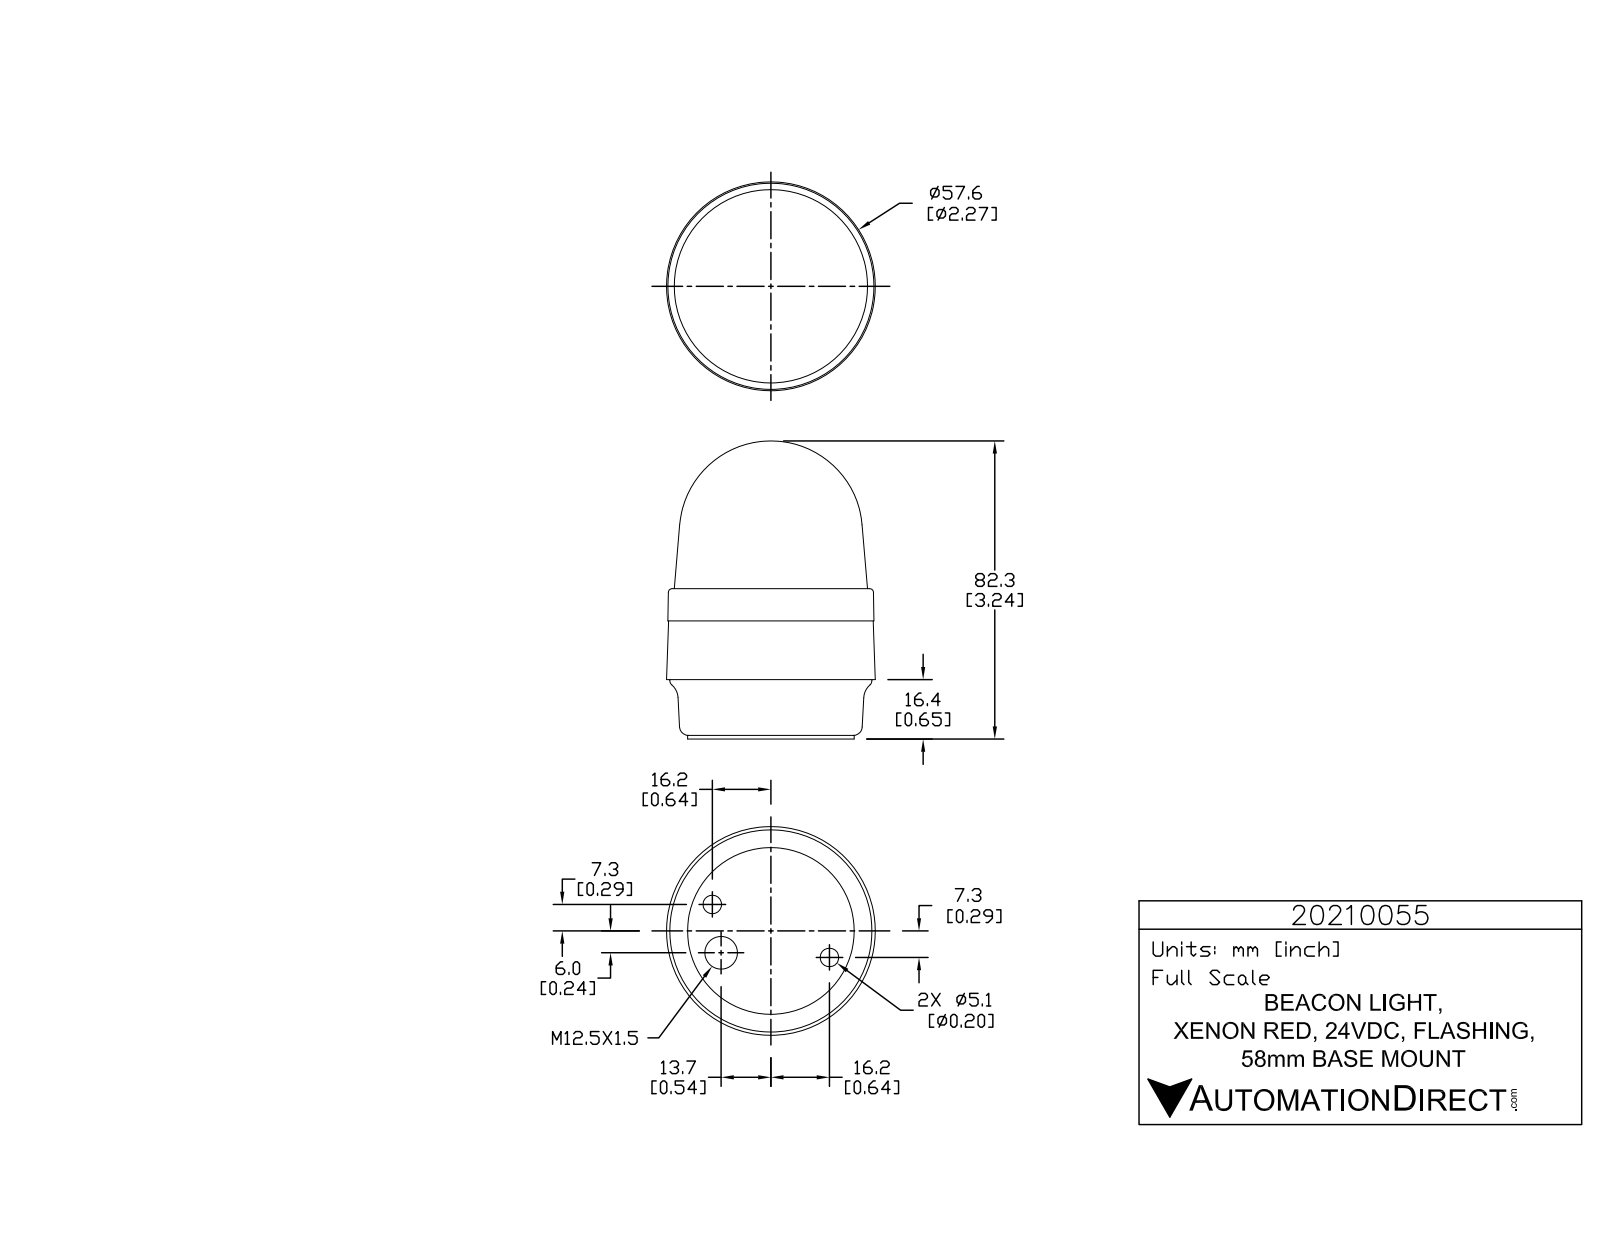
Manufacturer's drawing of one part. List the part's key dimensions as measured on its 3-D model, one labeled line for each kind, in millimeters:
Part name (STEP PRODUCT): 20210055
STEP written by: SolidWorks 2015 (AUTOMOTIVE_DESIGN)
Units: millimetres
Bodies: 1 solid, 763 faces (527 planar, 145 cylindrical, 91 other)
Overall size (bounding box): 82.3 × 57.63 × 57.63
Volume: 164 395 mm³ · Surface area: 16 261 mm²
Round holes (diameter × count): ⌀0.99 ×3, ⌀5.11 ×2, ⌀9 ×1
Round bosses / shafts (diameter × count): ⌀5.74 ×3, ⌀1.43 ×3, ⌀55.8 ×1, ⌀46 ×1
Partial cylindrical surfaces — rounded edges, fillets, slot ends (radius × count): R0.2 ×6, R0.21 ×6, R0.21 ×6, R3.32 ×6, R0.1 ×3, R0.12 ×3, R0.19 ×3, R0.2 ×3
Main face-to-face distances: 16.4, 1, 15.4, 41.5, 40.5, 25.1, 32.6, 31.6, 16.2, 8.9
Hole centre spacings: 13.56, 29.94, 35.5
